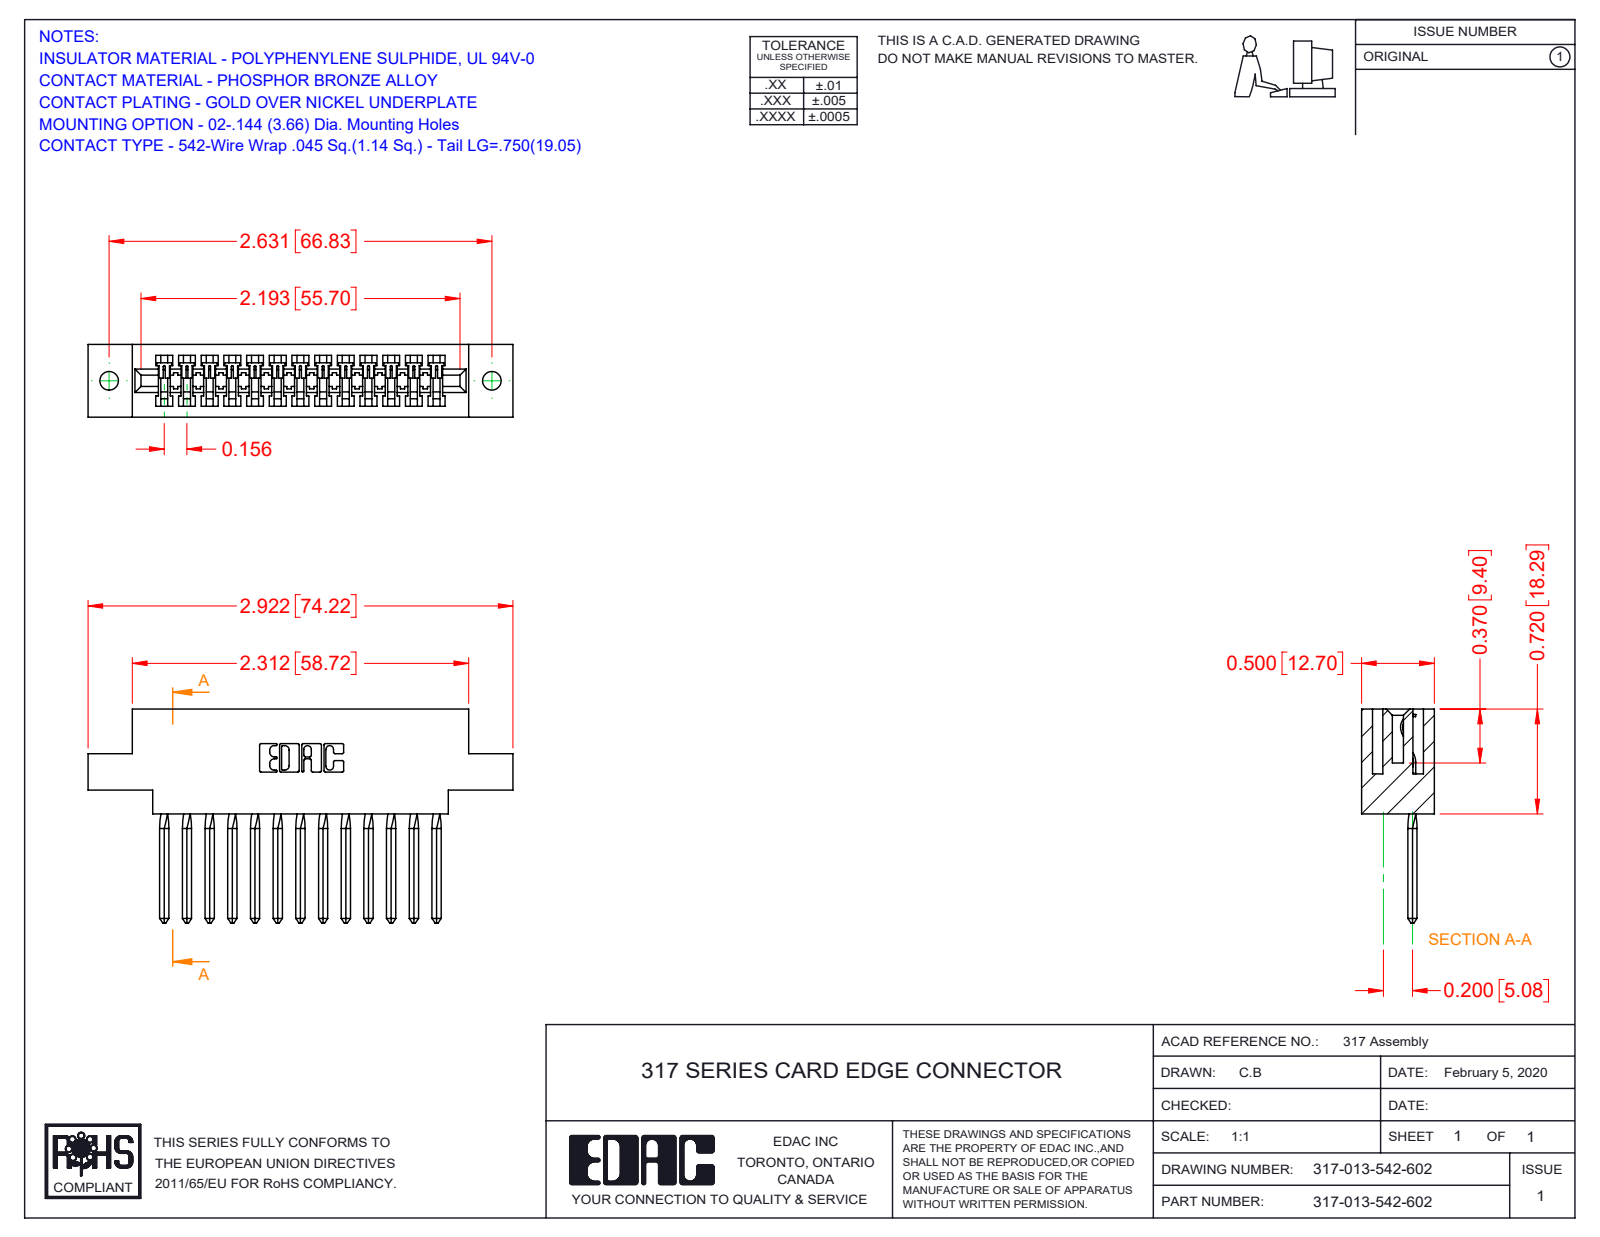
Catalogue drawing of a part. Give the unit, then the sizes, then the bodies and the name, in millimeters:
Units: millimetres
Overall size (bounding box): 74.2 × 37.3 × 12.7
Round holes (diameter × count): ⌀3.3 ×2
Partial cylindrical surfaces — rounded edges, fillets, slot ends (radius × count): R0.2 ×26, R0.3 ×22, R0.2 ×6, R0.8 ×6, R0.7 ×3, R1.9 ×1, R2.3 ×1, R2.5 ×1
Main face-to-face distances: 12.7, 1.9, 10.8, 2.8, 1.7, 8.9, 5.6, 3.5, 18.3, 8.4
Hole centre spacings: 66.8
Volume: 10 700 mm³ · Surface area: 12 080 mm²
Bodies: 14 solids, 1077 faces (890 planar, 135 cylindrical, 52 other)
Part name (STEP PRODUCT): 317-013-542-602; 317-290-003_542; 317 Part_.144 Dia
STEP written by: SolidWorks 2016 (CONFIG_CONTROL_DESIGN)
